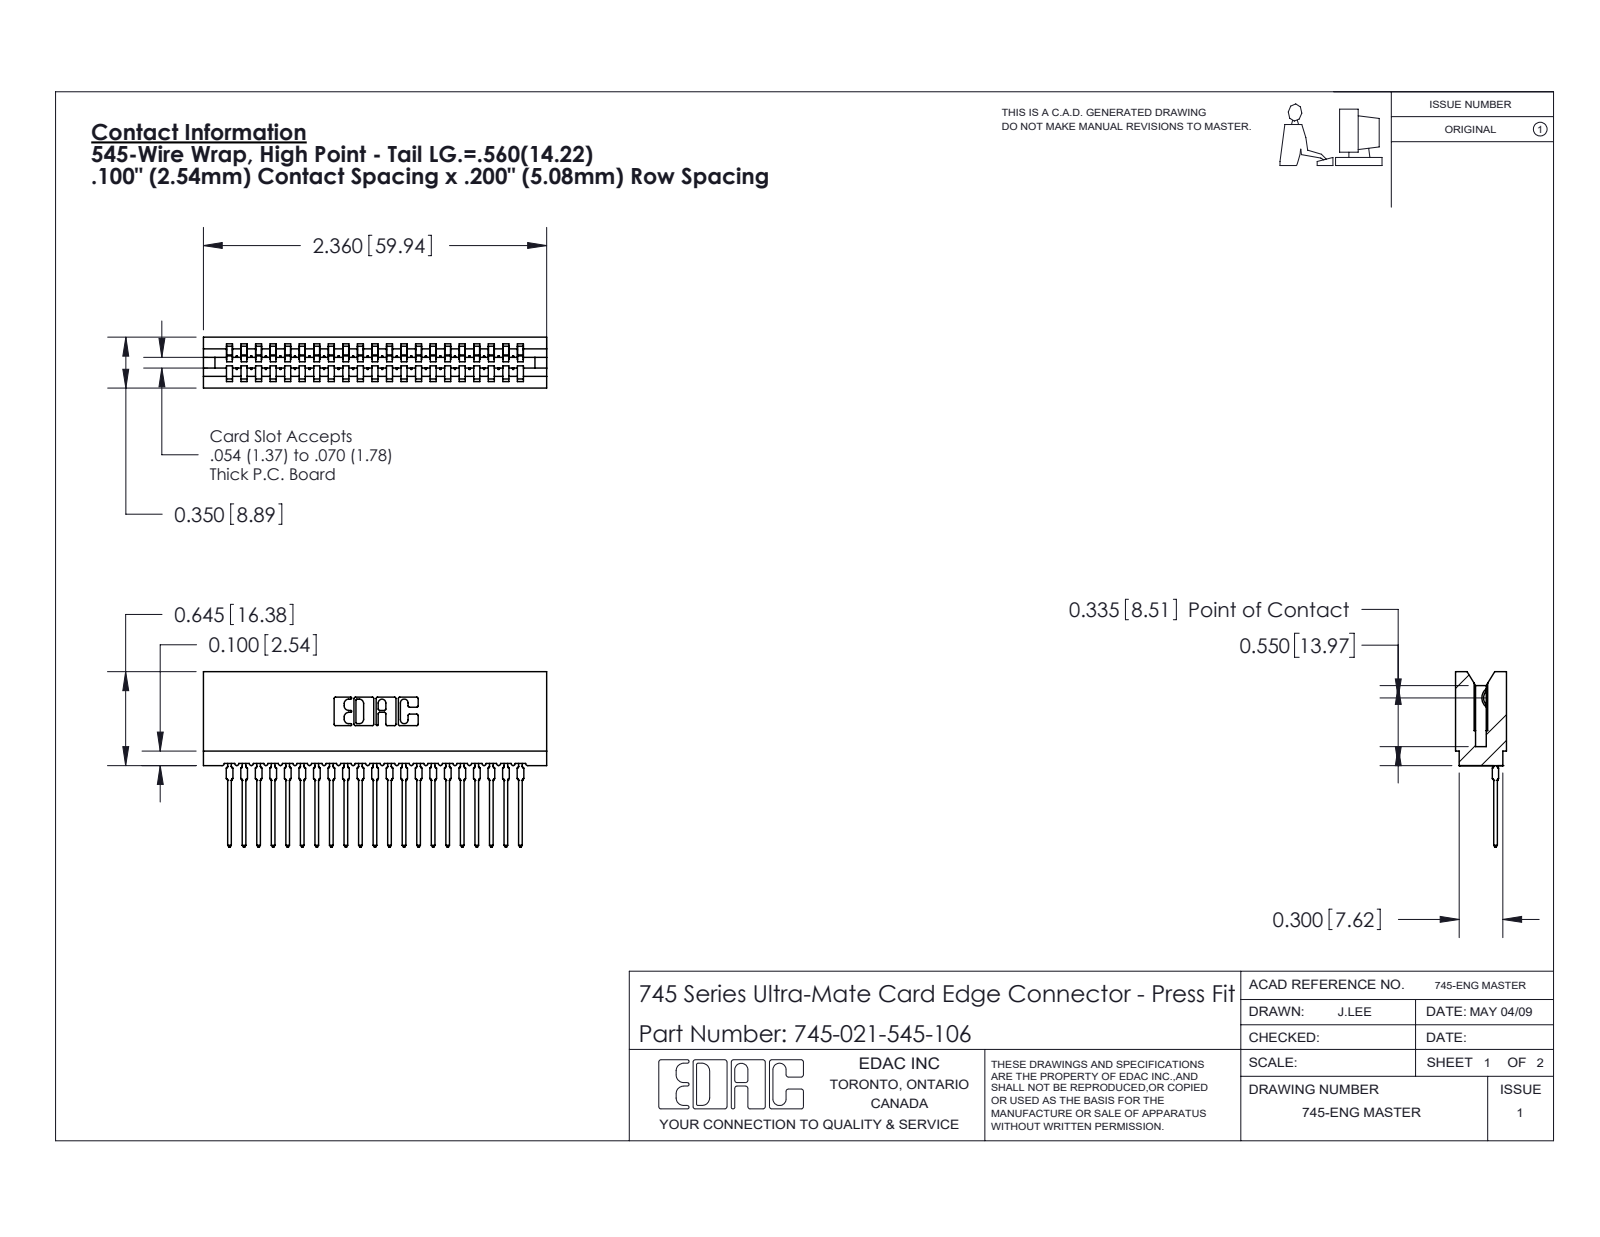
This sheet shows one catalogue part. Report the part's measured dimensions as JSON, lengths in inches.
{"part_name": "745 Part_Insulator Option - 06; 745-292-001_545; 745-021-545-106", "step_written_by": "SolidWorks 2020 (CONFIG_CONTROL_DESIGN)", "units": "inches", "bodies": {"solids": 22, "faces": 2448, "planar": 1463, "cylindrical": 439, "other": 546}, "overall_size": [2.36, 1.206, 0.35], "volume_in3": 0.328, "surface_area_in2": 15.39, "partial_cylinders_radius": [[0.015, 42], [0.021, 42], [0.01, 22], [0.007, 6], [0.031, 6], [0.005, 4], [0.011, 4], [0.026, 3]], "face_to_face_distances": [0.1, 0.2, 0.3, 0.4, 0.35, 0.5, 0.6, 0.7, 0.138, 0.212]}
